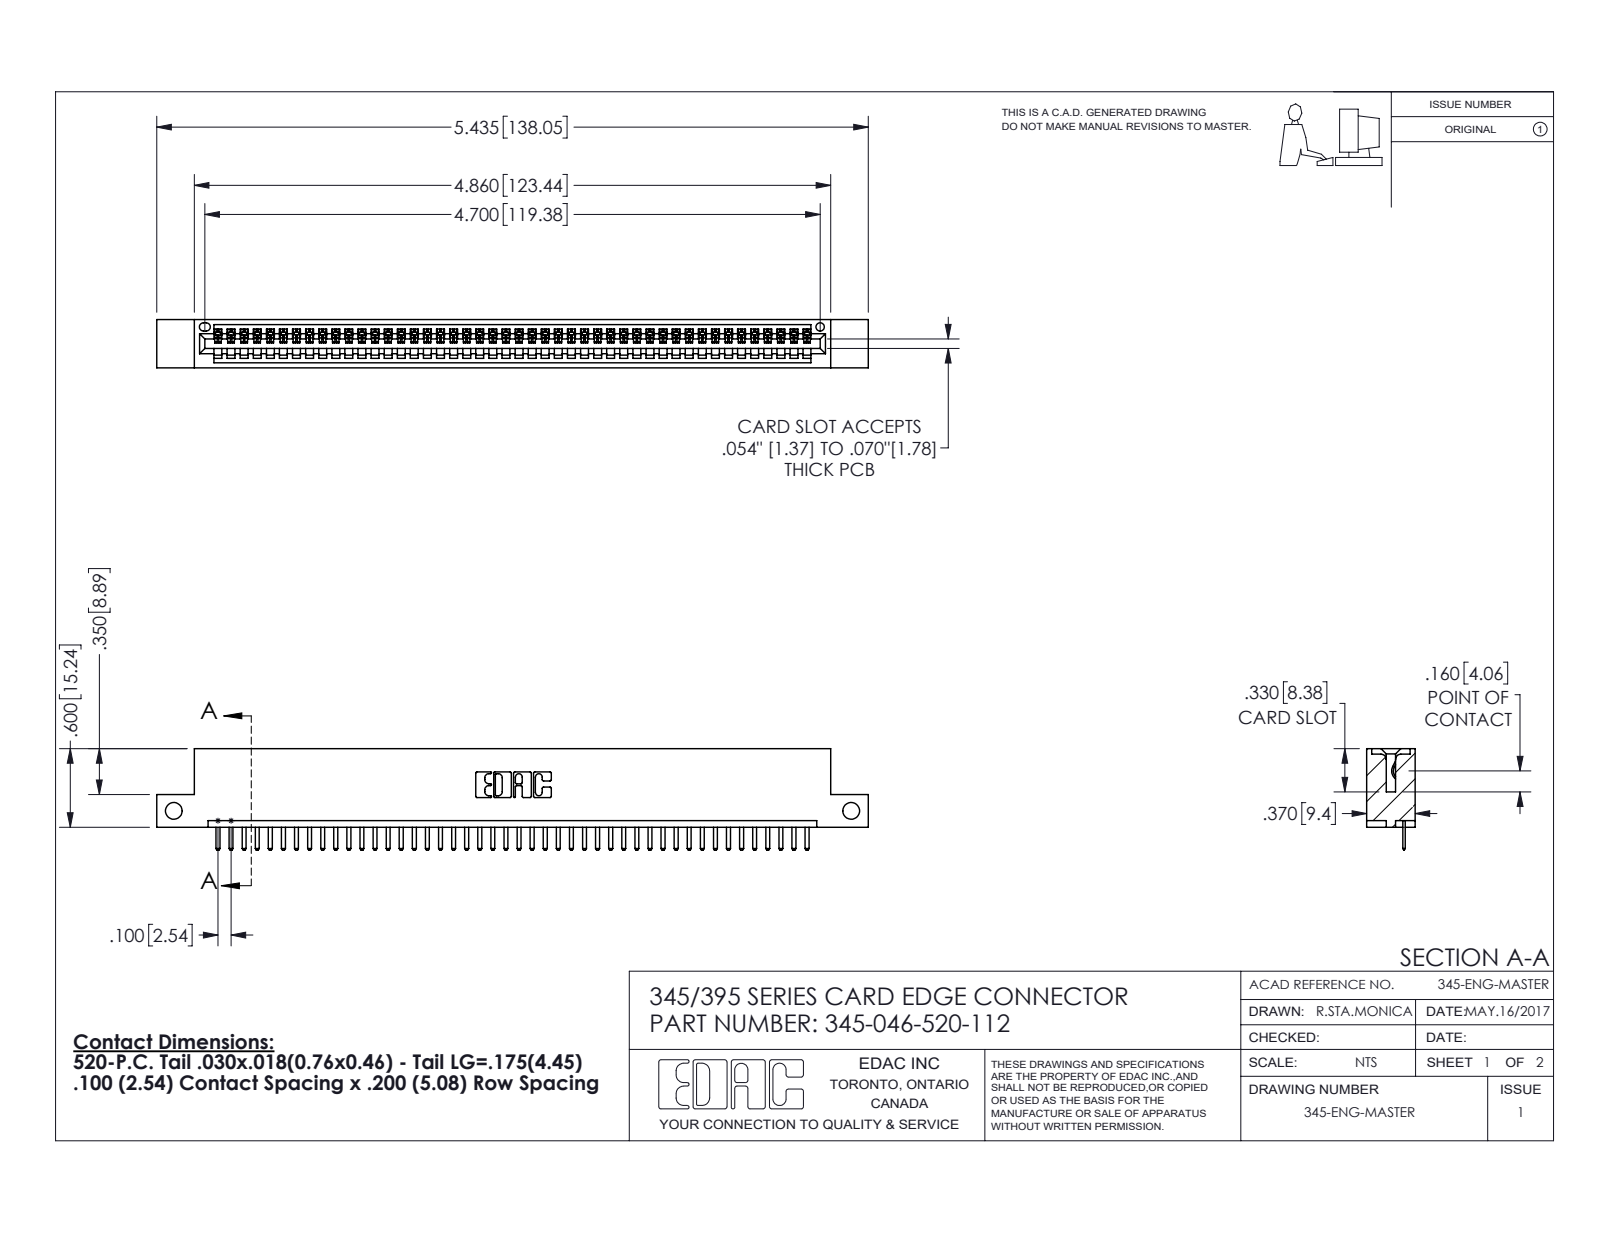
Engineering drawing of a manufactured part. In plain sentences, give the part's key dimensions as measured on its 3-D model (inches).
The part is named "345-046-520-112; 345-292-001_345-293-120; 345 Part_Flush Mounting Lugs - Side Mount". Its 3-D file was written by "SolidWorks 2016 (CONFIG_CONTROL_DESIGN)". It is 47 solids with 2978 faces: 2012 planar, 966 cylindrical and 0 other. Overall it measures 5.435 by 0.775 by 0.37 inches. Its volume is 0.789 cubic inches and its surface area 25.82 square inches. Round holes: 2 of diameter 0.128, 1 of diameter 0.064. Partial cylindrical surfaces (rounded edges, fillets, slot ends): 94 of radius 0.01, 92 of radius 0.006, 22 of radius 0.01, 6 of radius 0.007, 6 of radius 0.031, 3 of radius 0.026, 2 of radius 0.031, 2 of radius 0.04. The main face-to-face distances are 0.298, 0.072, 0.37, 0.2, 0.098, 0.272, 0.025, 0.225, 0.072, 0.149. The hole center spacings are 5.175.
